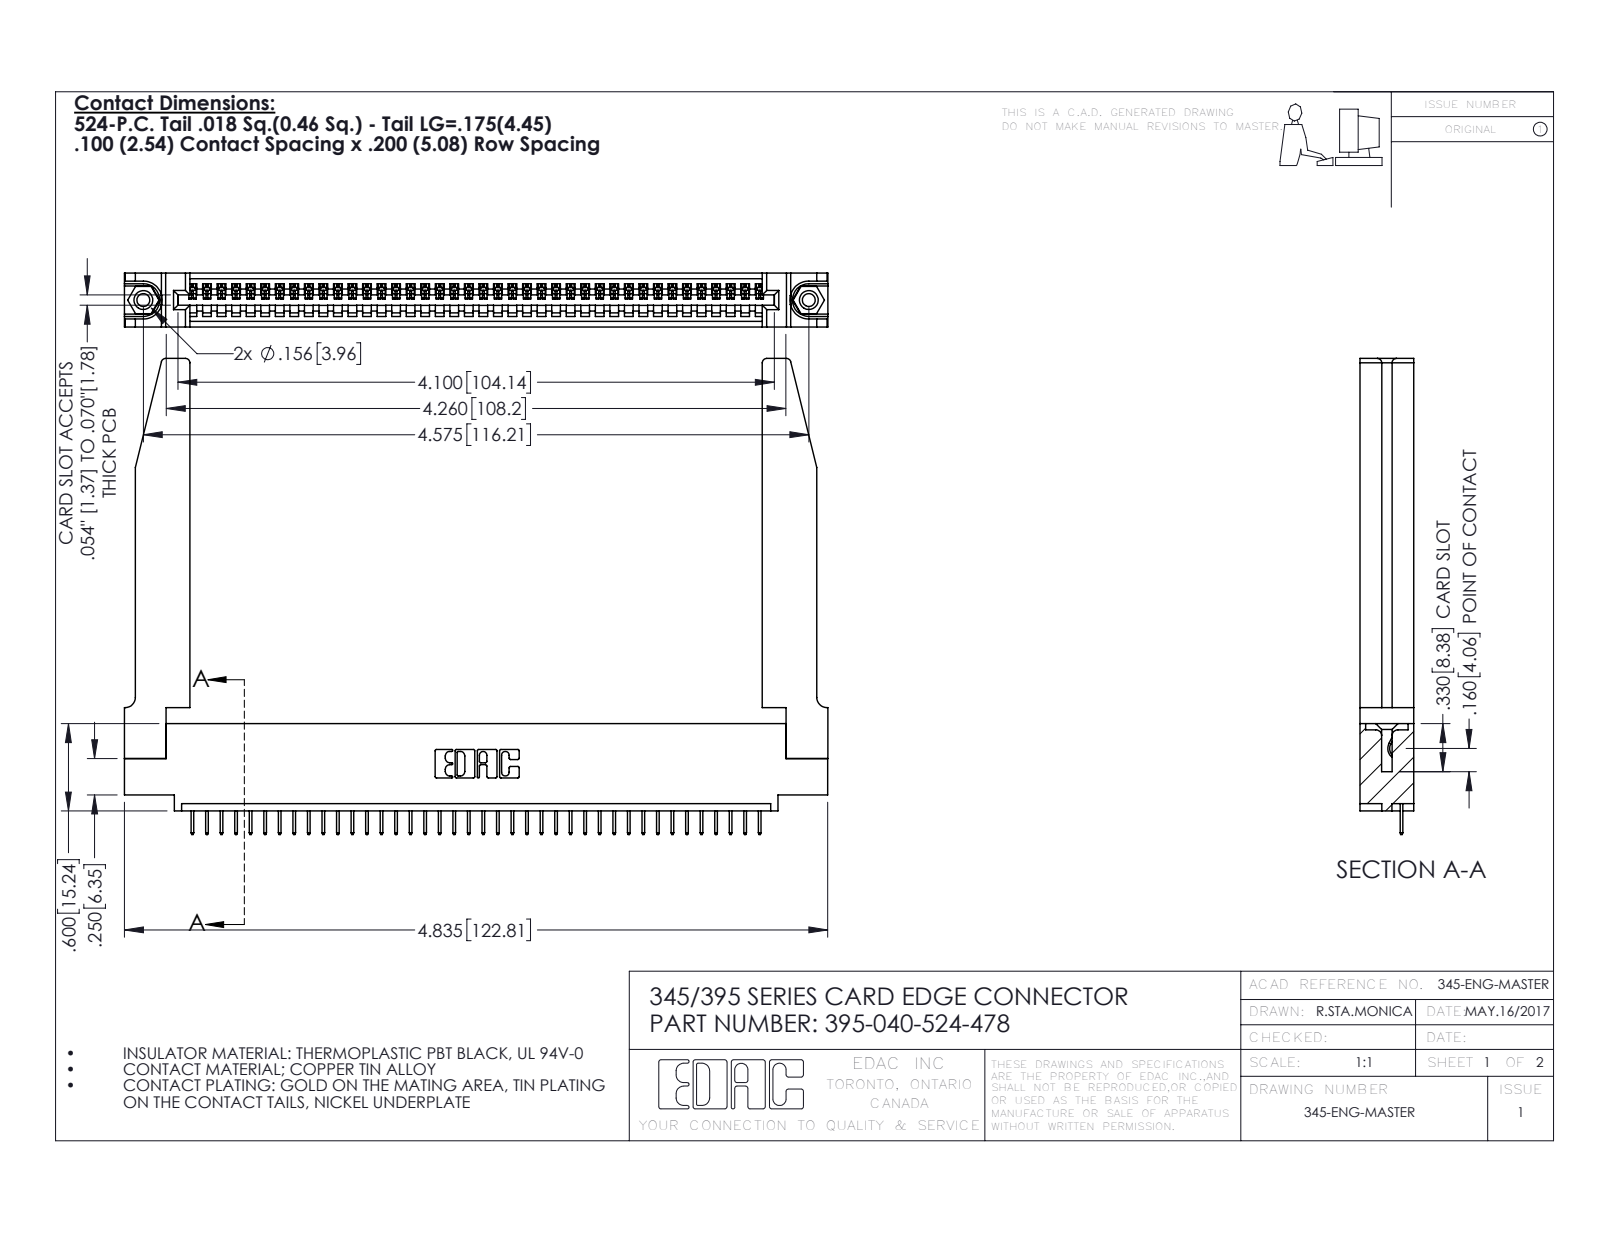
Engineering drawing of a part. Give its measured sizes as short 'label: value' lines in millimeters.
name: 395-040-524-478; 345-250-001_345-250-001-102; 345-220-078_345-220-078; 345-292-001_345-293-124 (+1 more)
written by: SolidWorks 2016 (CONFIG_CONTROL_DESIGN)
unit: mm
bodies: 45 solids, 2844 faces (2066 planar, 726 cylindrical, 52 other)
size: 122.8 × 83.1 × 9.4
volume: 19 190 mm³; area: 21 570 mm²
holes: 2× ⌀2.3, 2× ⌀3.2, 2× ⌀4, 1× ⌀1.6
bosses: 2× ⌀3.9
rounds: 80× R0.2, 22× R0.3, 8× R0.8, 6× R0.2, 6× R0.8, 3× R0.7, 2× R0.8, 2× R1
face distances: 9.4, 1.8, 7.6, 5.1, 2.5, 6.9, 0.6, 5.7, 3.8, 3.8
hole spacings: 6.9, 110.2, 116.2
